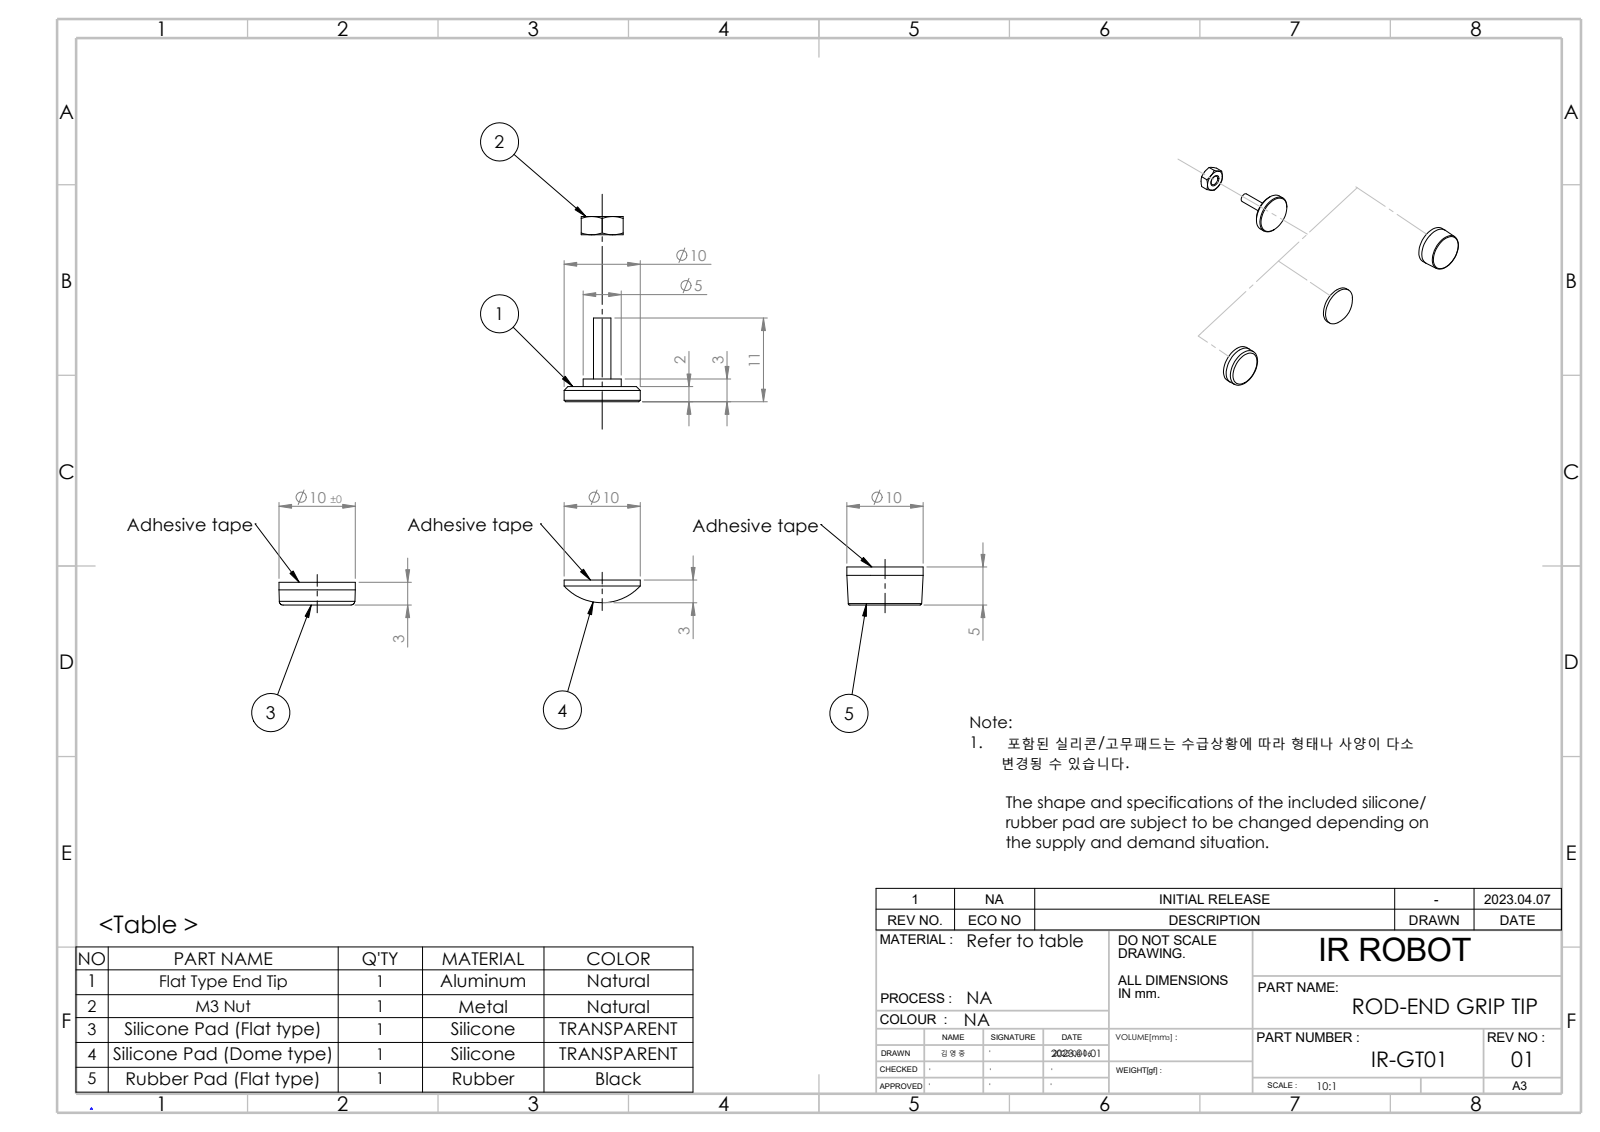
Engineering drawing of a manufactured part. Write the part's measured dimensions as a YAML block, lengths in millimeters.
part_name: "Silicone Pad (Flat type)_D10_3T; Silicone Pad (Dome type)_D10_3T; M3 Nut; Rubber Pad (Flat type)_D10_5T (+2 more)"
step_written_by: "SolidWorks 2016 (AUTOMOTIVE_DESIGN)"
units: millimeters
bodies: {solids: 5, faces: 63, planar: 17, cylindrical: 16, other: 30}
overall_size: [84.53, 50.98, 27.38]
volume: 1023
surface_area: 1127
round_holes:
  - {diameter: 2.5, count: 1}
  - {diameter: 3, count: 1}
round_bosses_or_shafts:
  - {diameter: 10, count: 4}
  - {diameter: 5, count: 1}
  - {diameter: 2.3, count: 1}
face_to_face_distances: [2, 23.67, 3, 26.67, 5, 1.7, 3.3, 21.67, 23.37, 25.37]
